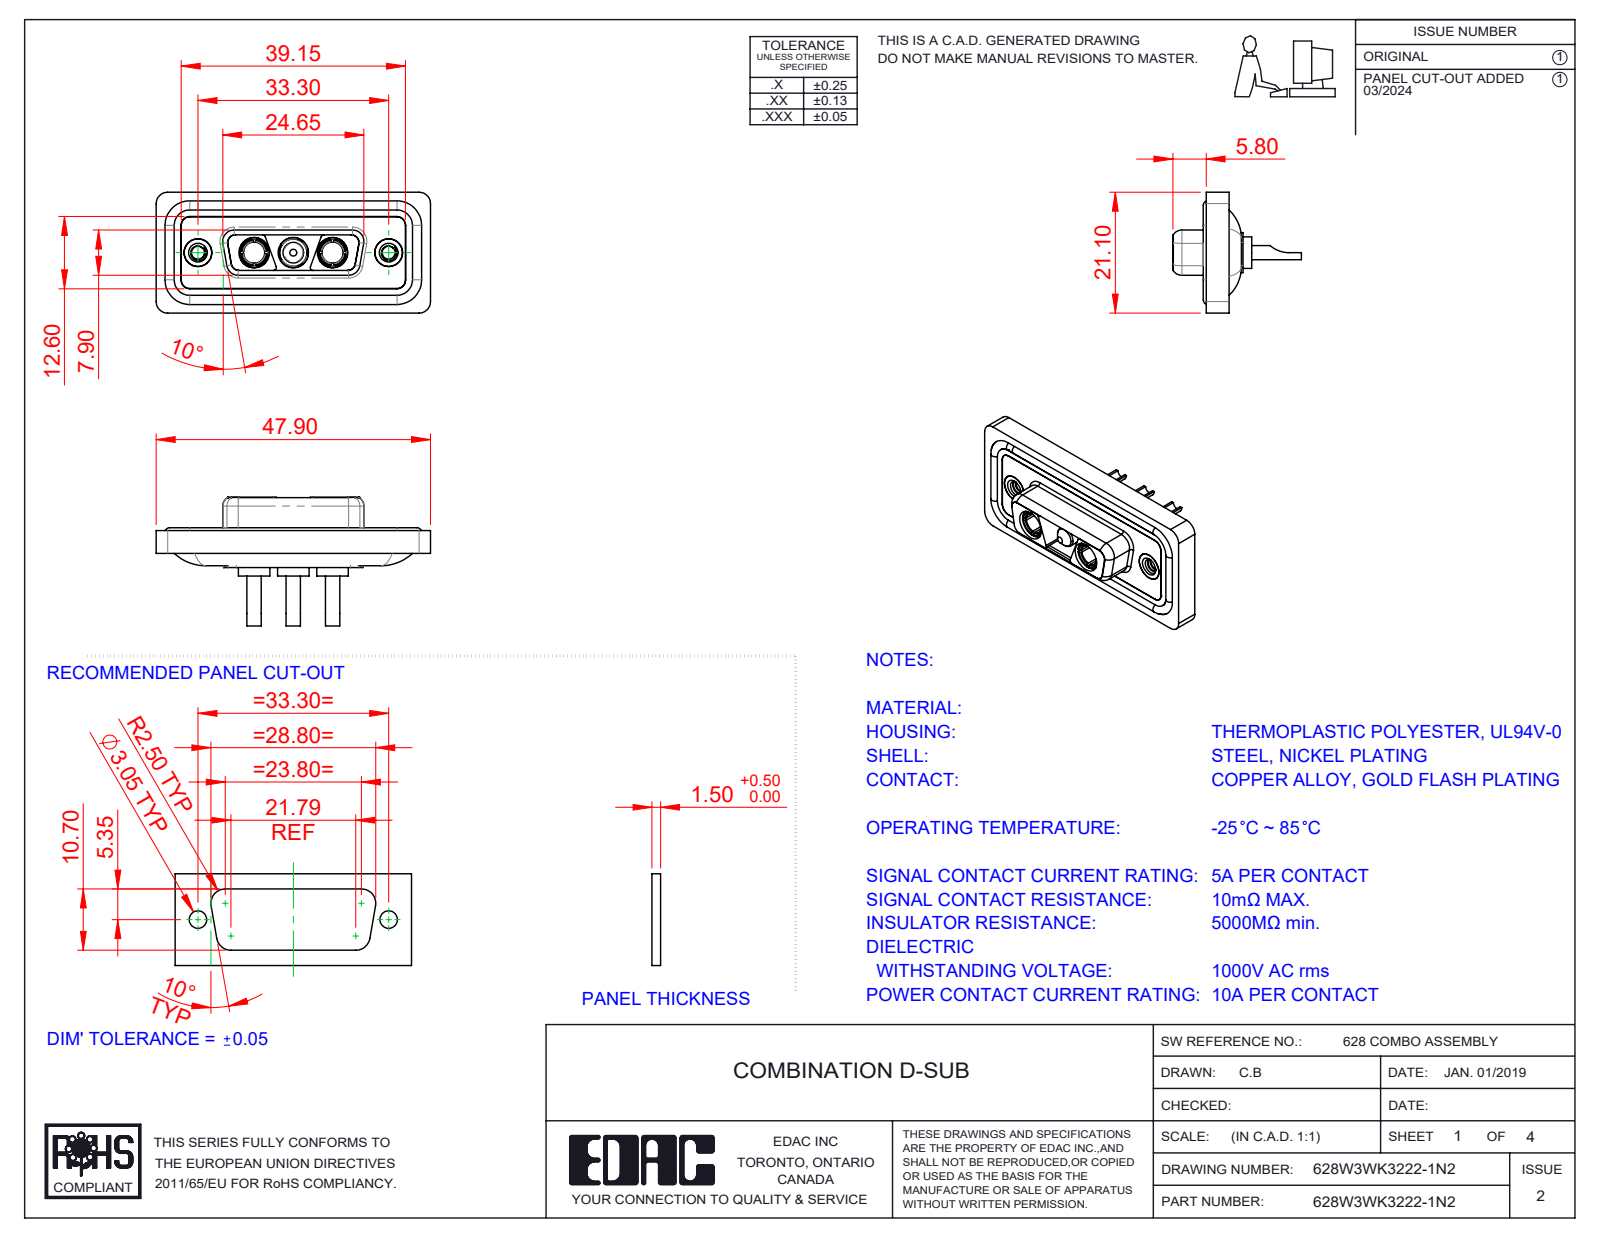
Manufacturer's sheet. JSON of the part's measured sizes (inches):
{"part_name": "628W3WK3222-1N2; 628Combo Waterproof Housing_15 Contacts; 628Combo Housing_3WK3; 628Combo Shell Front_15 Contacts (+4 more)", "step_written_by": "SolidWorks 2023 (CONFIG_CONTROL_DESIGN)", "units": "inches", "bodies": {"solids": 13, "faces": 599, "planar": 184, "cylindrical": 267, "other": 148}, "overall_size": [1.886, 0.884, 0.831], "volume_in3": 0.358, "surface_area_in2": 14.95, "round_holes": [[0.191, 5], [0.067, 3], [0.209, 3], [0.089, 2], [0.146, 2], [0.157, 2], [0.159, 2], [0.197, 2]], "round_bosses_or_shafts": [[0.063, 4], [0.217, 3], [0.205, 3], [0.187, 3], [0.148, 3], [0.098, 3], [0.195, 2], [0.195, 2]], "partial_cylinders_radius": [[0.059, 22], [0.079, 20], [0.053, 12], [0.02, 8], [0.063, 8], [0.01, 4], [0.024, 4], [0.026, 4]], "face_to_face_distances": [0.016, 0.063, 0.071, 0.02, 0.043, 0.114, 0.222, 0.278, 0.059, 0.211], "hole_center_spacings": [0.27, 0.386, 0.656, 0.925, 0.539, 1.311]}
